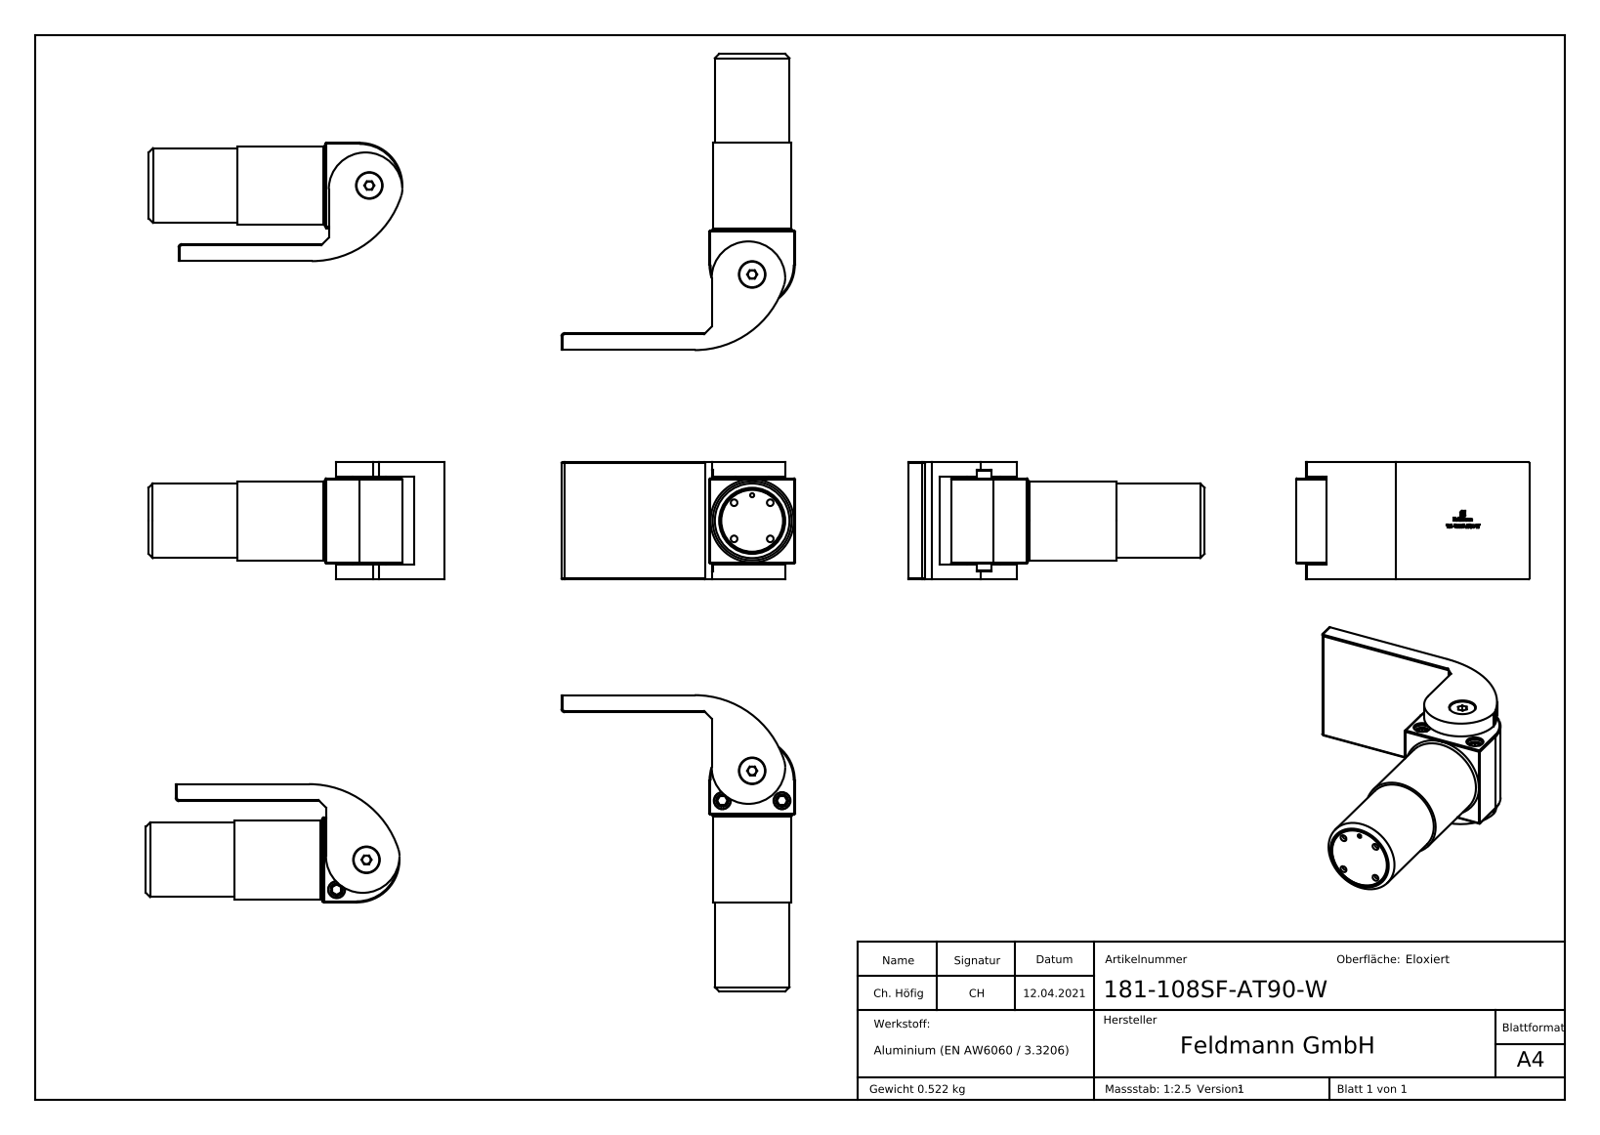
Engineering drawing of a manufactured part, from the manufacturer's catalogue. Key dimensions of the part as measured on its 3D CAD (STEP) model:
Part name (STEP PRODUCT): 181-108SF-AT90-W; DIN-7991 M3-M10_DIN7991 M6x14; Teil2; DIN-7991 M3-M10 (+3 more)
STEP written by: SolidWorks 2018 (CONFIG_CONTROL_DESIGN)
Units: millimetres
Bodies: 6 solids, 607 faces (301 planar, 90 cylindrical, 216 other)
Overall size (bounding box): 14000.45 × 5999.86 × 5999.7
Volume: 191 592 mm³ · Surface area: 38 742 mm²
Round holes (diameter × count): ⌀3.1 ×4, ⌀8 ×2, ⌀1.9 ×1, ⌀5 ×1, ⌀6.5 ×1, ⌀12.5 ×1, ⌀15.7 ×1, ⌀24 ×1, ⌀29.7 ×1
Round bosses / shafts (diameter × count): ⌀7.8 ×2, ⌀37 ×1, ⌀35 ×1, ⌀29.5 ×1, ⌀26 ×1, ⌀23.6 ×1, ⌀15.5 ×1, ⌀12 ×1
Partial cylindrical surfaces — rounded edges, fillets, slot ends (radius × count): R0.5 ×12, R1.5 ×1, R10 ×1, R17.25 ×1, R20 ×1, R44.11 ×1
Main face-to-face distances: 8, 48, 7, 55, 47.5, 0.5, 7.5, 40.5, 40, 14.5
Hole centre spacings: 12.01, 16.98, 9.19, 19.8, 22.18, 24.01, 12, 28
